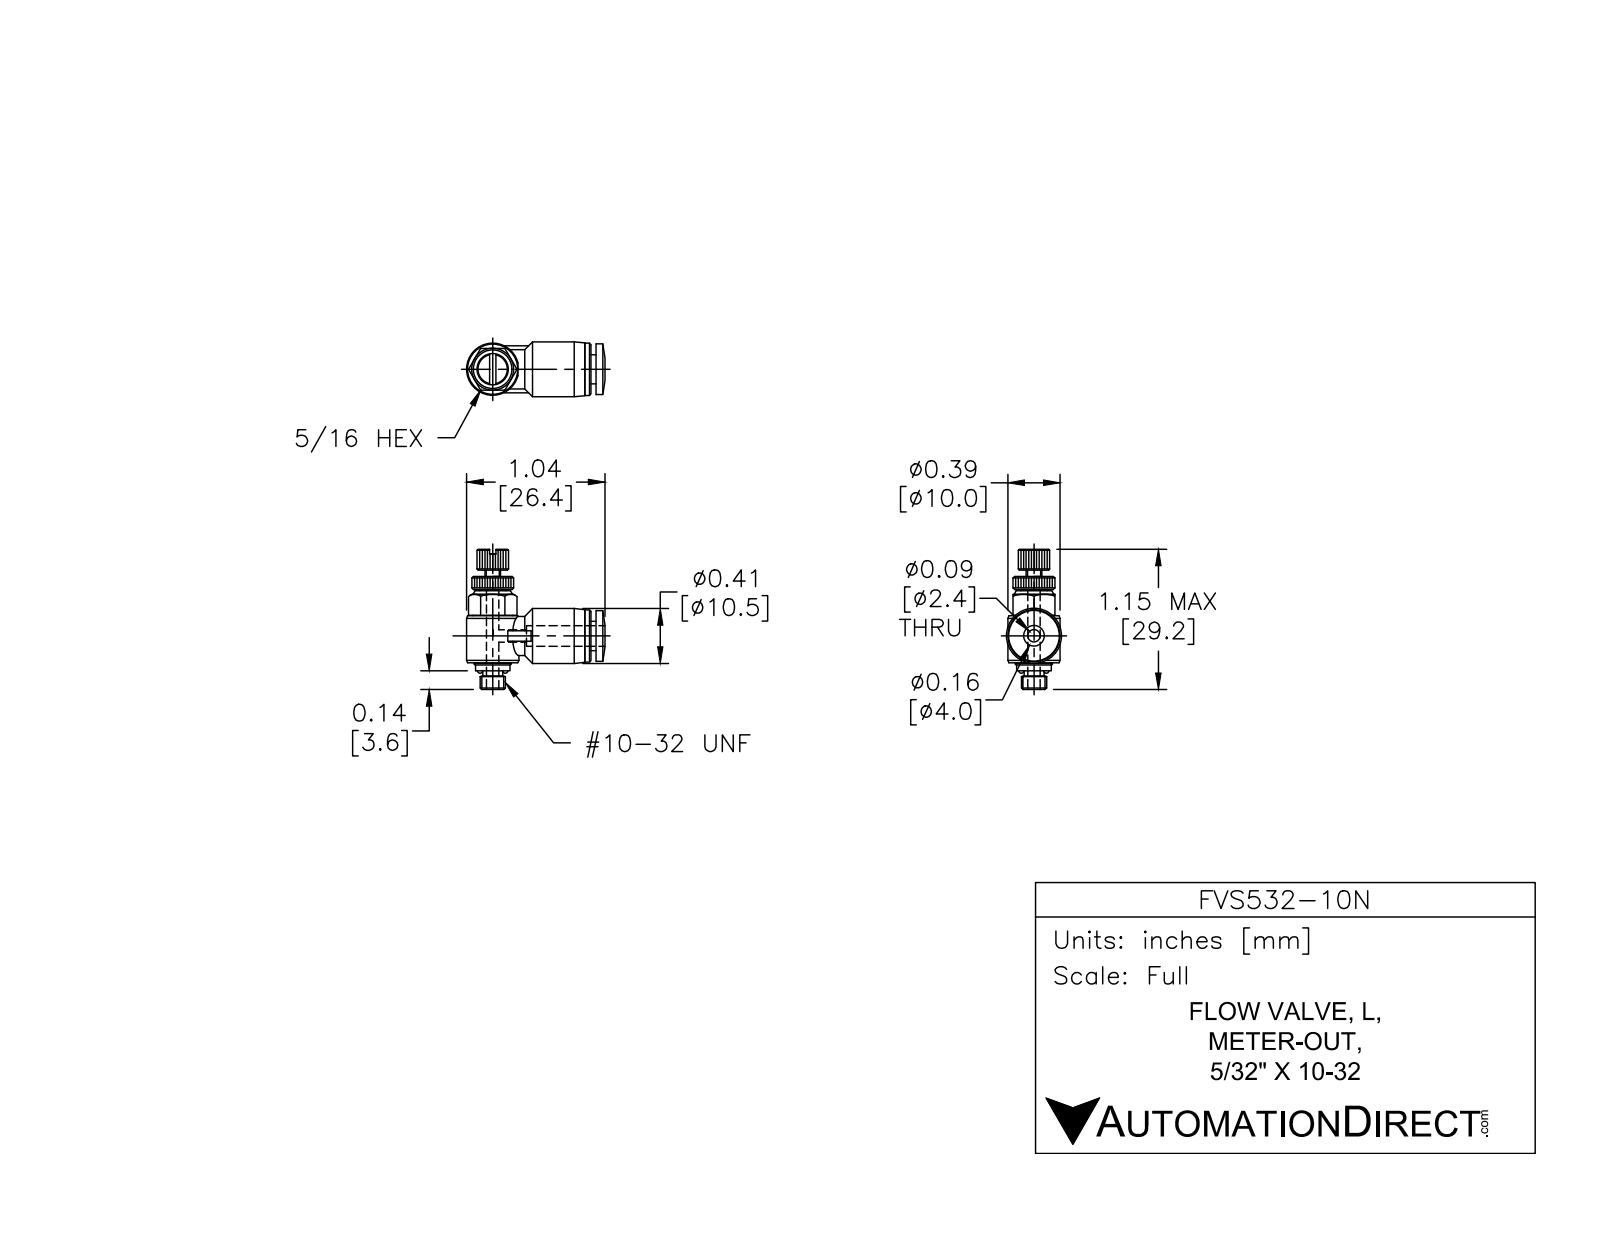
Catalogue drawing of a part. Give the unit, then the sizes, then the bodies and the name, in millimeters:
Units: millimetres
Overall size (bounding box): 29.1 × 25.3 × 10.5
Round holes (diameter × count): ⌀1.5 ×2, ⌀3.8 ×1, ⌀4.3 ×1
Round bosses / shafts (diameter × count): ⌀10 ×2, ⌀10.5 ×1, ⌀9.9 ×1, ⌀7.6 ×1, ⌀7.1 ×1, ⌀6.7 ×1, ⌀6.7 ×1, ⌀6.6 ×1
Partial cylindrical surfaces — rounded edges, fillets, slot ends (radius × count): R3 ×1, R4 ×1
Main face-to-face distances: 8, 0.9, 16.6, 9, 5.2, 7.4, 7.5, 4, 14.1, 14
Volume: 2 230 mm³ · Surface area: 1 923 mm²
Bodies: 2 solids, 345 faces (149 planar, 97 cylindrical, 99 other)
Part name (STEP PRODUCT): FVS532-10N
STEP written by: SolidWorks 2015 (AUTOMOTIVE_DESIGN)
